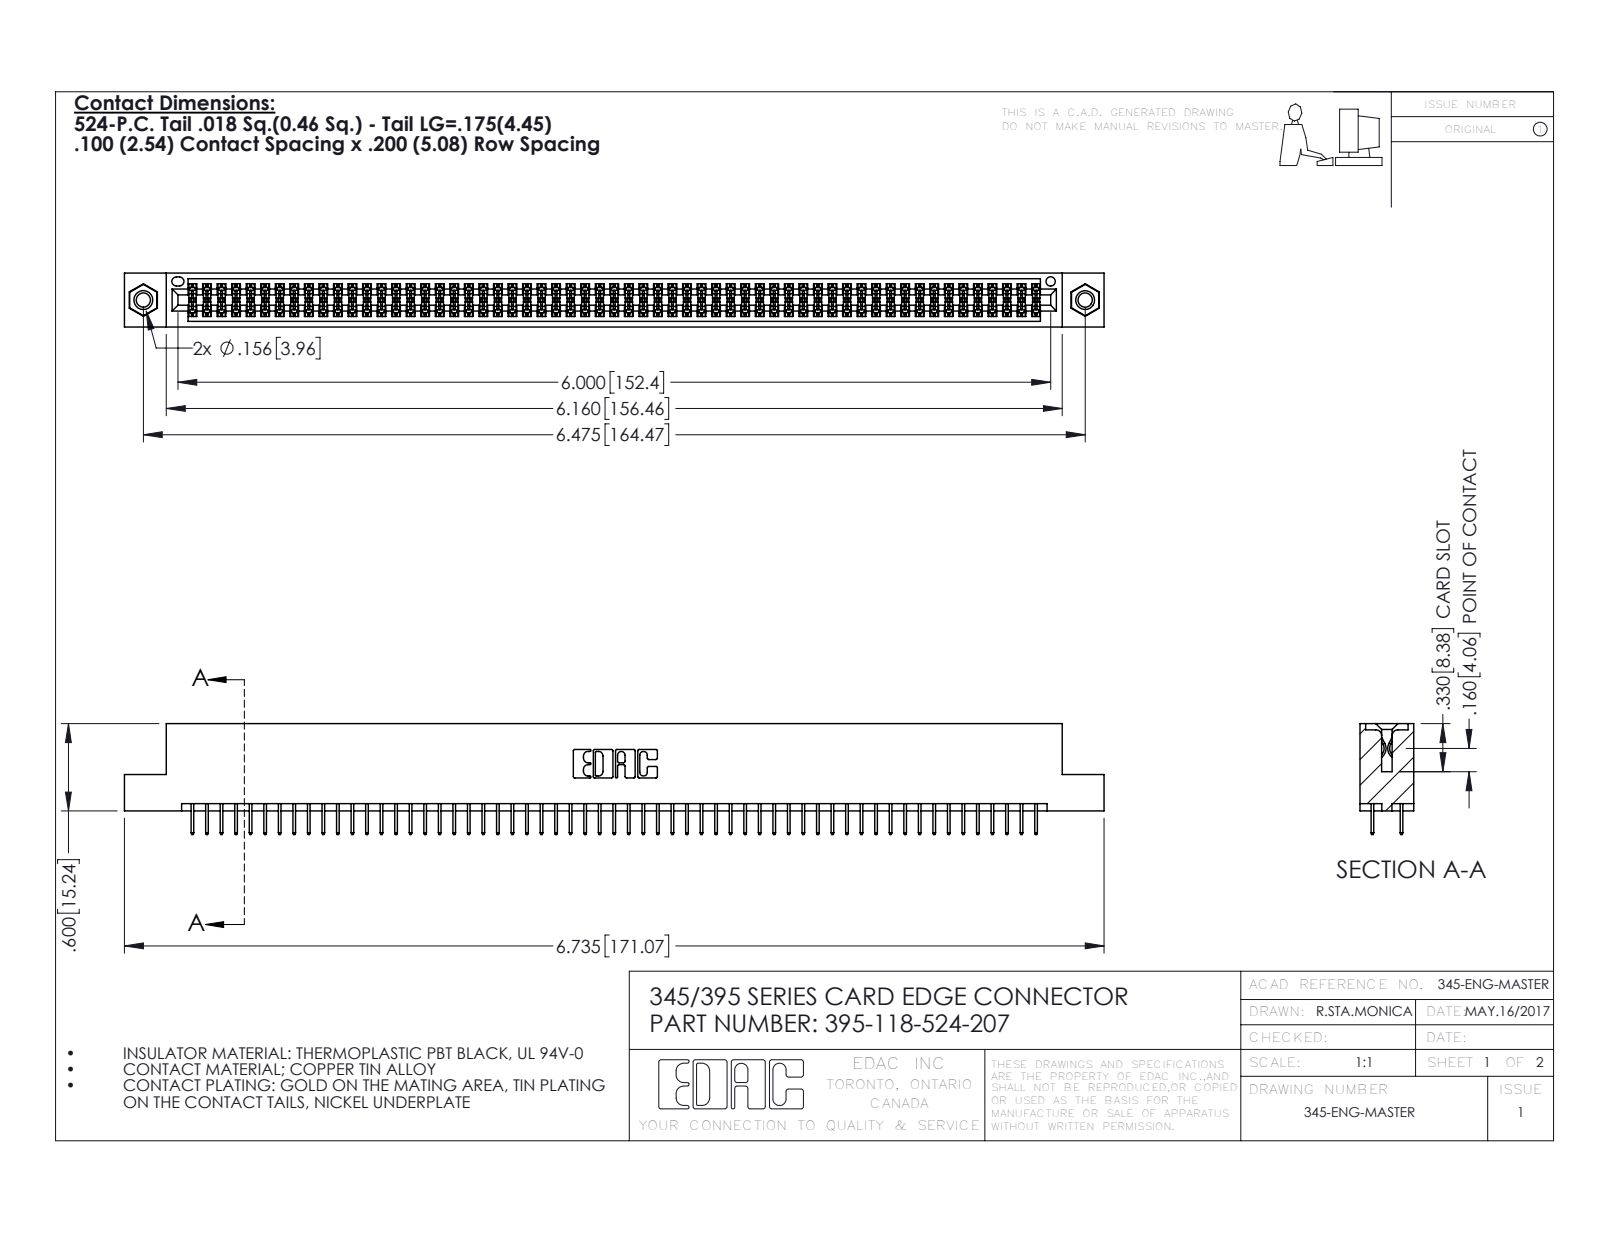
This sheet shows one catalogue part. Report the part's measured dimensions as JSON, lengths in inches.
{"part_name": "345-292-001_345-293-124; 345 Part_Flush Mounting Lugs - 0.156 Dia-TI; 345-250-001_345-250-005-103; 395-118-524-207", "step_written_by": "SolidWorks 2016 (CONFIG_CONTROL_DESIGN)", "units": "inches", "bodies": {"solids": 121, "faces": 6558, "planar": 4714, "cylindrical": 1828, "other": 16}, "overall_size": [6.735, 0.762, 0.37], "volume_in3": 1.012, "surface_area_in2": 37.82, "round_holes": [[0.098, 2], [0.125, 2], [0.156, 2], [0.064, 1]], "round_bosses_or_shafts": [[0.155, 2]], "partial_cylinders_radius": [[0.006, 177], [0.01, 22], [0.007, 6], [0.031, 6], [0.026, 3], [0.014, 2], [0.019, 2], [0.022, 2]], "face_to_face_distances": [0.072, 0.298, 0.2, 0.37, 0.098, 0.272, 0.025, 0.225, 0.072, 0.175], "hole_center_spacings": [0.27, 6.239, 6.475]}
